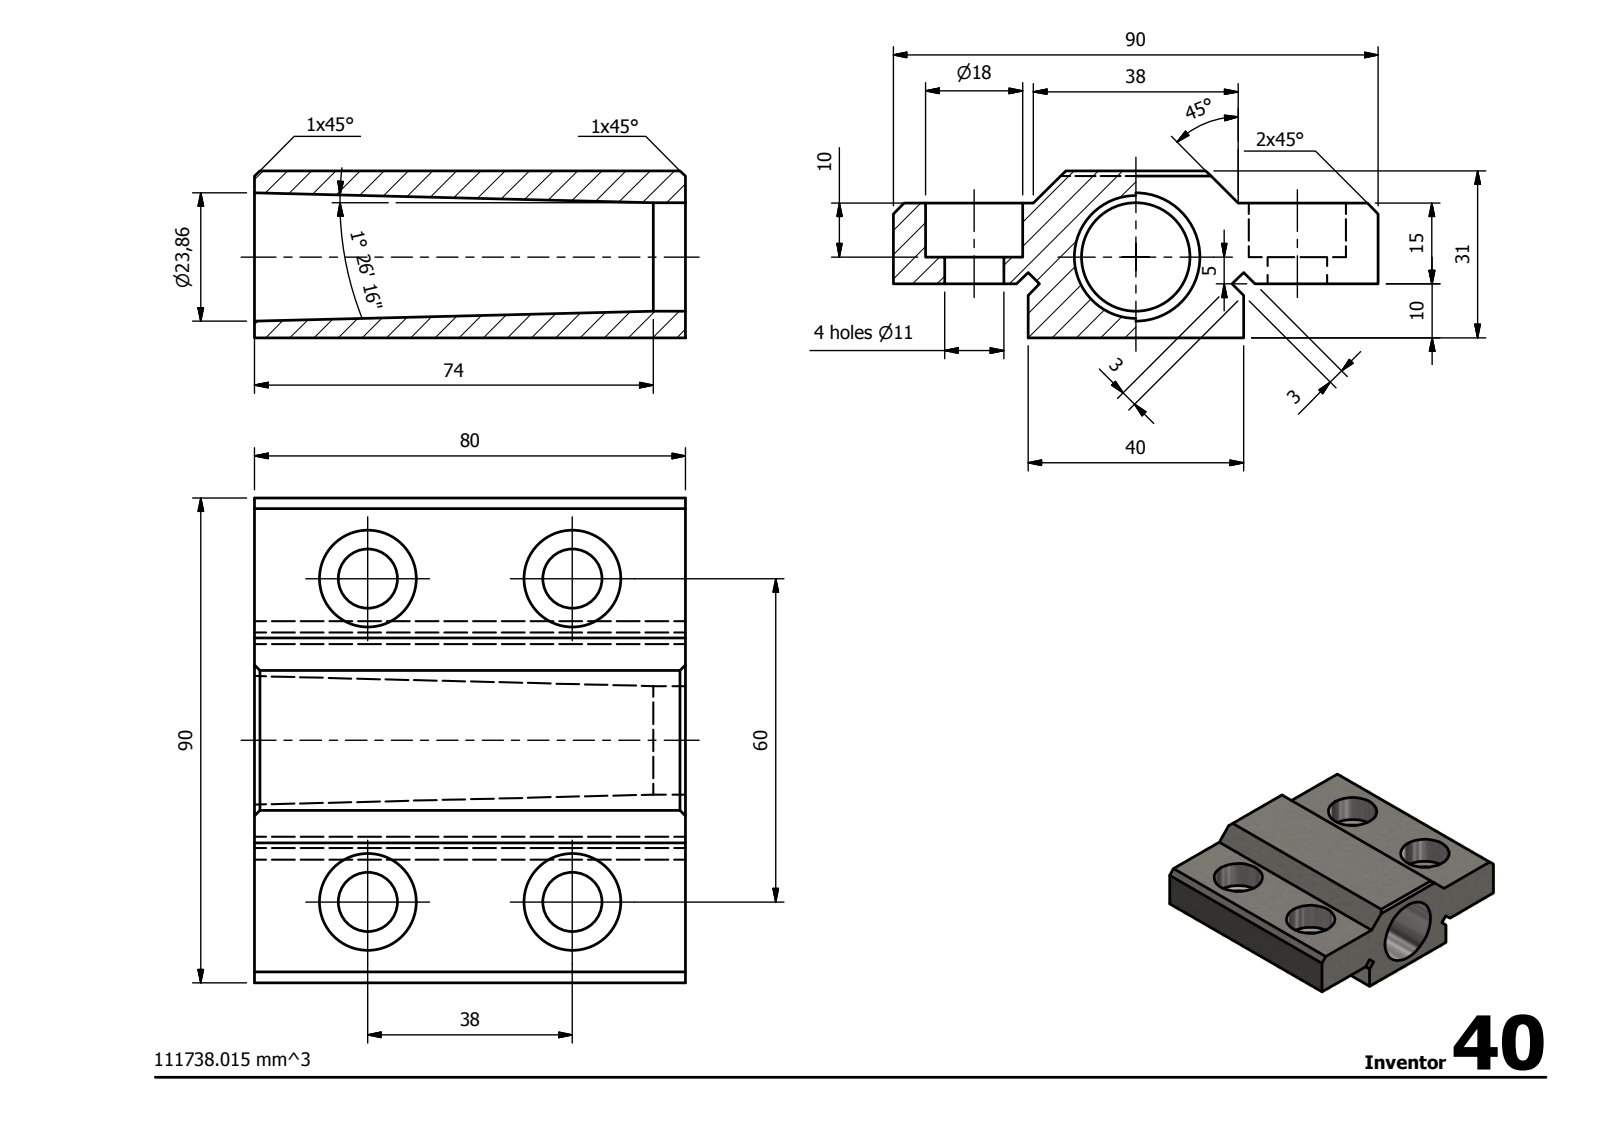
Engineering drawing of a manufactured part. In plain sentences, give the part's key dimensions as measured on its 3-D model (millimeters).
Its 3-D file was written by "Autodesk Inventor 2014 (AUTOMOTIVE_DESIGN)". It is 1 solid with 38 faces: 28 planar, 9 cylindrical and 1 other. Overall it measures 90 by 80 by 31 millimeters. Its volume is 111 738 cubic millimeters and its surface area 30 111 square millimeters. Round holes: 4 of diameter 11, 4 of diameter 18, 1 of diameter 20.15. The main face-to-face distances are 25, 10, 15, 31, 21, 6, 80, 65, 90, 5. The hole center spacings are 38, 60, 71.02.
